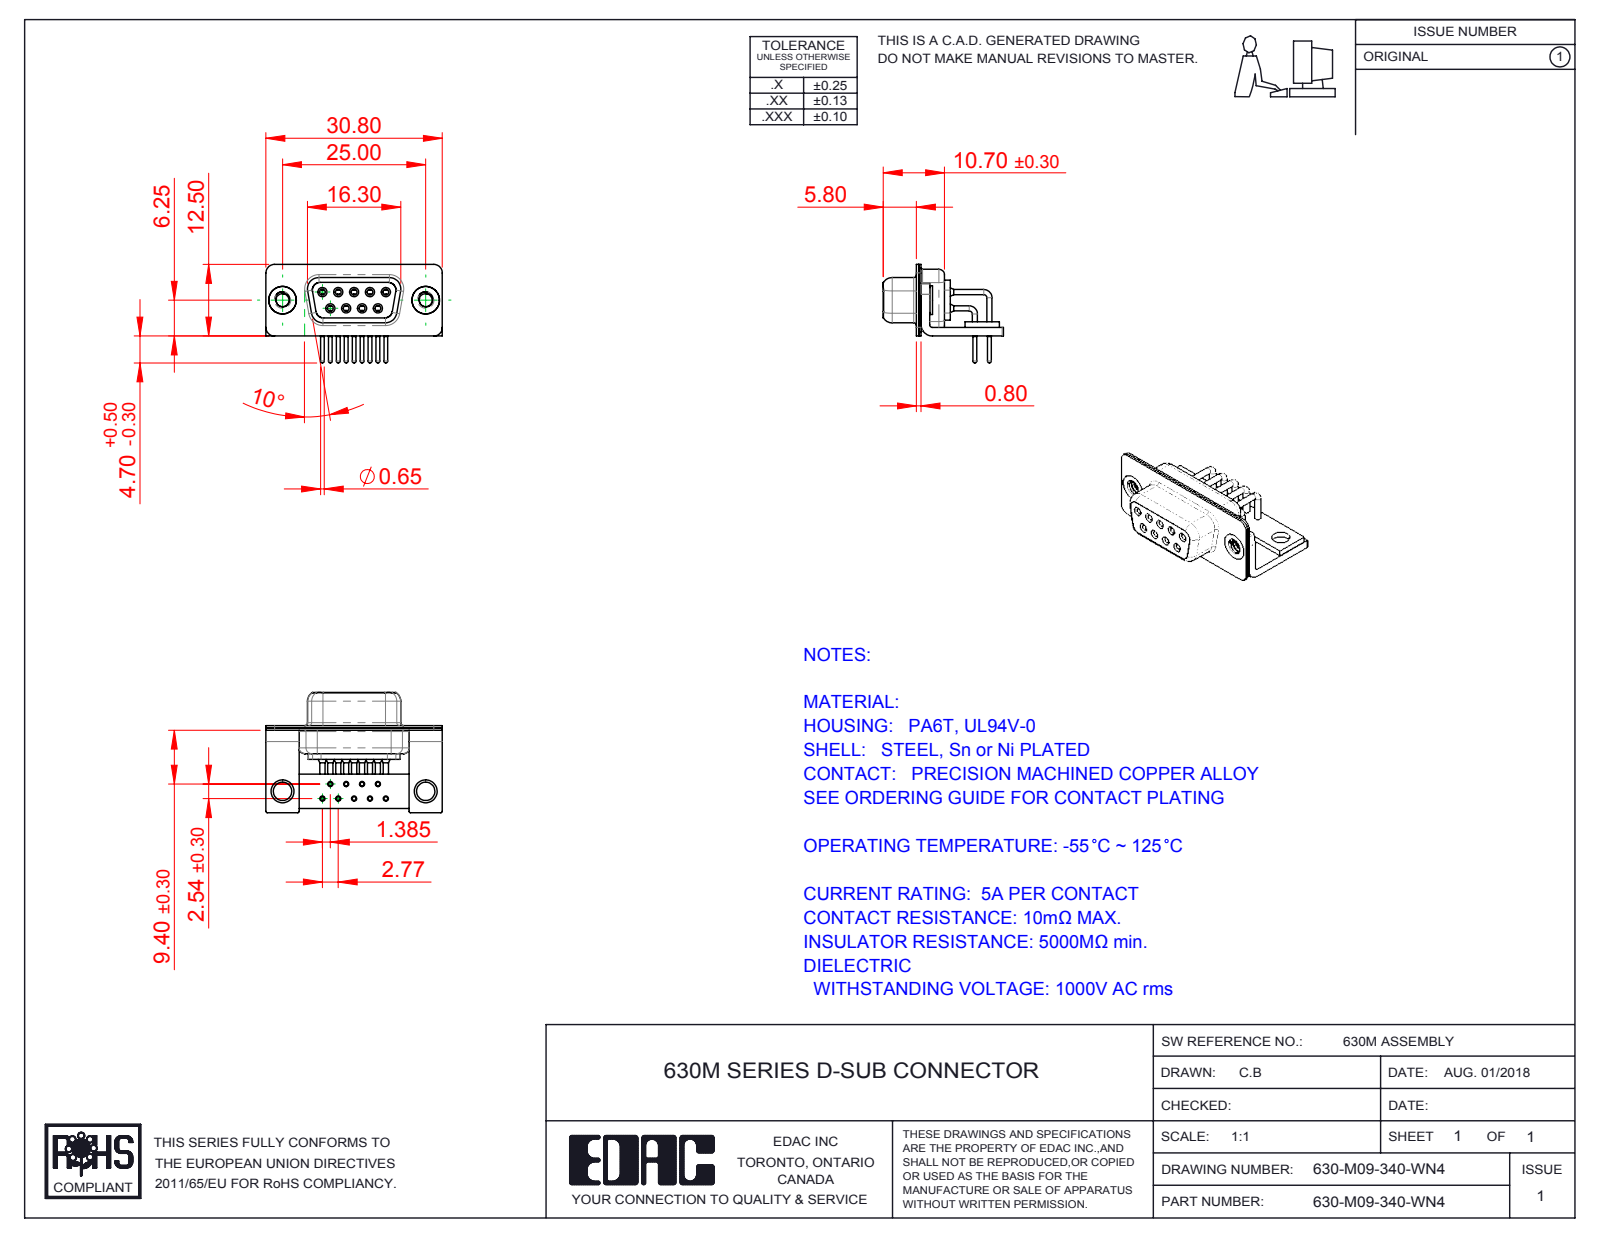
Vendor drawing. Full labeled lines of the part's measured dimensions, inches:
Part name (STEP PRODUCT): 630-M09-340-WN4; 630M Stabilizer Board_09 Contacts; 630M Shell Rear_09 Contacts; 630M Housing_09 Contacts (+5 more)
STEP written by: SolidWorks 2016 (CONFIG_CONTROL_DESIGN)
Units: inches
Bodies: 17 solids, 824 faces (228 planar, 384 cylindrical, 212 other)
Overall size (bounding box): 1.213 × 0.827 × 0.677
Volume: 0.134 in³ · Surface area: 8.795 in²
Round holes (diameter × count): ⌀0.035 ×9, ⌀0.039 ×9, ⌀0.043 ×9, ⌀0.067 ×9, ⌀0.071 ×9, ⌀0.079 ×9, ⌀0.089 ×2, ⌀0.126 ×2, ⌀0.157 ×2, ⌀0.189 ×2
Round bosses / shafts (diameter × count): ⌀0.063 ×9, ⌀0.059 ×9, ⌀0.035 ×9, ⌀0.026 ×9, ⌀0.197 ×2, ⌀0.193 ×2
Partial cylindrical surfaces — rounded edges, fillets, slot ends (radius × count): R0.01 ×16, R0.059 ×16, R0.079 ×13, R0.053 ×8, R0.063 ×8, R0.02 ×5, R0.024 ×4, R0.026 ×4
Main face-to-face distances: 0.016, 0.031, 0.059, 0.091, 0.075, 0.039, 0.368, 0.057, 0.098, 0.352
Hole centre spacings: 0.109, 0.218, 0.124, 0.192, 0.327, 0.114, 0.114, 0.198
